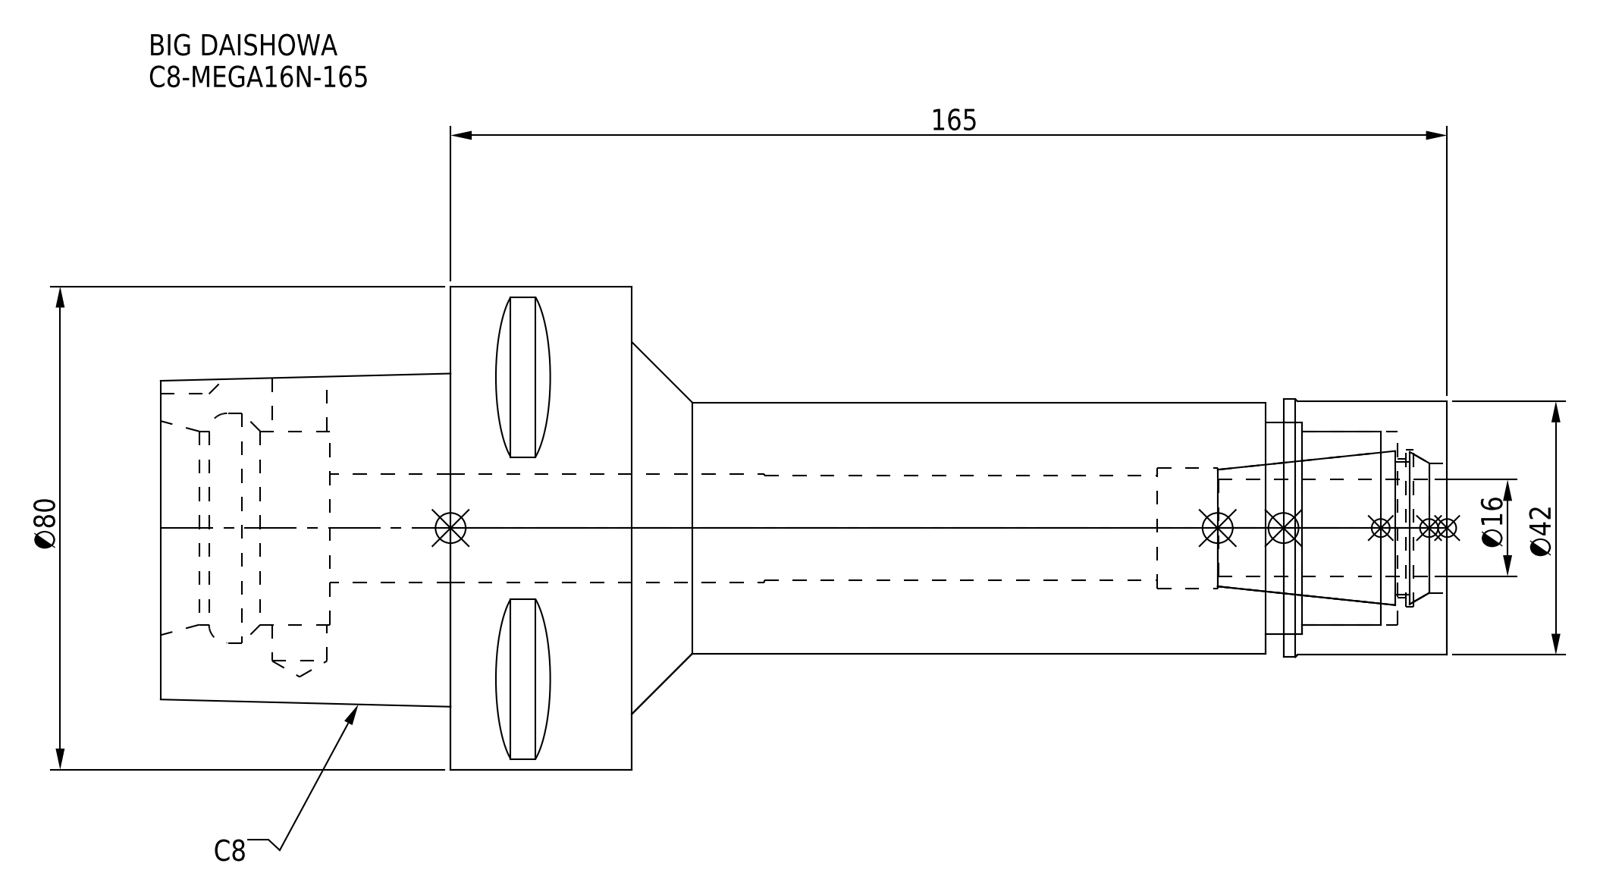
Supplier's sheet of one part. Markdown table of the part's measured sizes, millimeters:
| quantity | value |
| --- | --- |
| part name | DXF_TEMP_ASSY_ASM_4_ASM.stp; C8-MEGA16N-165-160.stp; MGN16_1.stp; C8-MEGA16N-165 (+3 more) |
| STEP written by | SolidWorks 2019 (CONFIG_CONTROL_DESIGN) |
| units | millimeters |
| bodies | 2 solids, 95 faces (38 planar, 39 cylindrical, 18 other) |
| overall size | 213 × 80 × 80 |
| volume | 367 872 mm³ |
| surface area | 62 415 mm² |
| round holes (diameter × count) | 9.1 × 1, 17.3 × 1, 18 × 1, 20 × 1, 21.5 × 1, 23 × 1, 26 × 1, 32 × 1, 35 × 1, 38 × 1 |
| round bosses / shafts (diameter × count) | 80 × 1, 42.7 × 1, 42 × 1, 41.6 × 1 |
| partial cylindrical surfaces (radius × count) | 6 × 1 |
| main face-to-face distances | 30, 48, 165, 78, 135, 213, 20, 185, 50, 28 |
